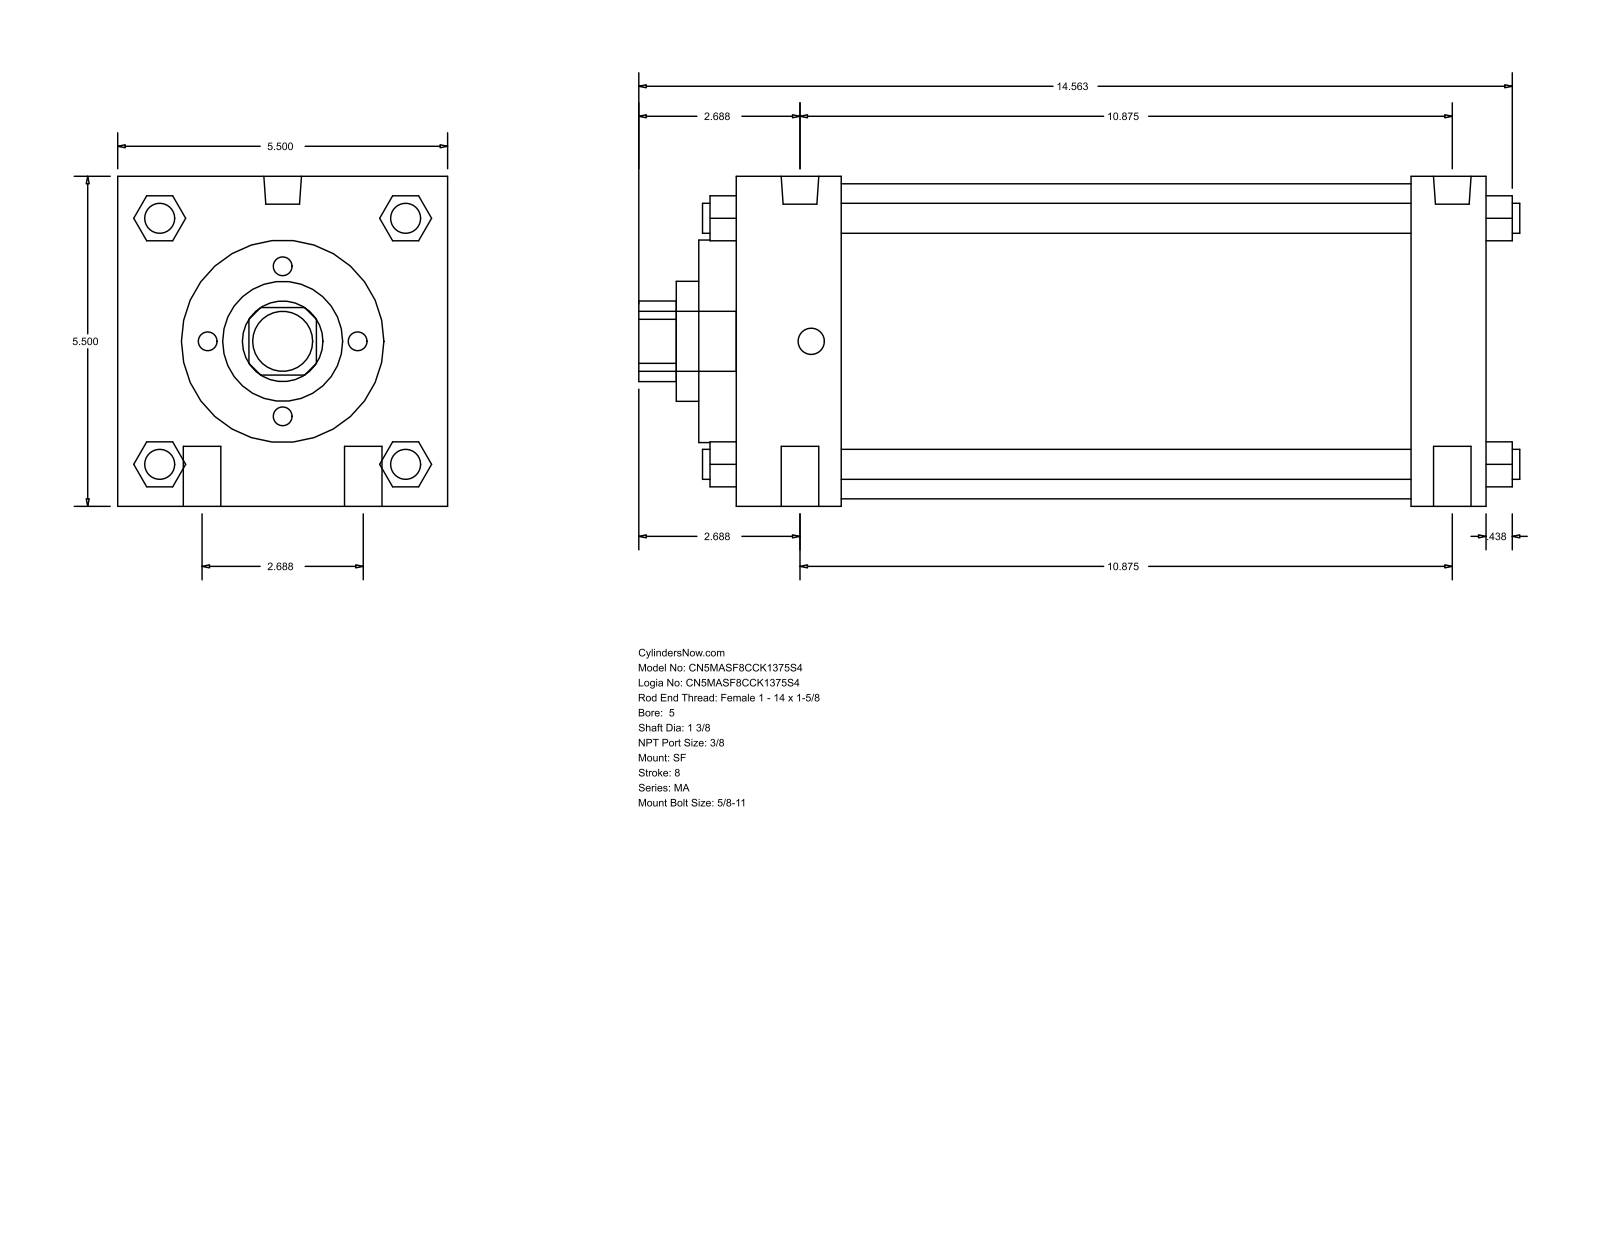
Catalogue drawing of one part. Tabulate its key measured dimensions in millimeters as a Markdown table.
| quantity | value |
| --- | --- |
| part name | MA_SF__0500_1.375 |
| STEP written by | GSSL Pune (CONFIG_CONTROL_DESIGN) |
| units | millimeters |
| bodies | 0 solids, 126 faces (95 planar, 31 cylindrical, 0 other) |
| overall size | 373.06 × 139.7 × 139.7 |
| round holes (diameter × count) | 34.92 × 1, 50.8 × 1, 85.72 × 1, 133.35 × 1 |
| round bosses / shafts (diameter × count) | 15.88 × 4, 12.7 × 4, 15.93 × 2, 11.11 × 2, 25.4 × 1 |
| partial cylindrical surfaces (radius × count) | 17.06 × 1 |
| main face-to-face distances | 139.7, 317.5, 44.45, 285.75, 241.3, 273.05, 31.75, 15.87, 60.32, 301.62 |
